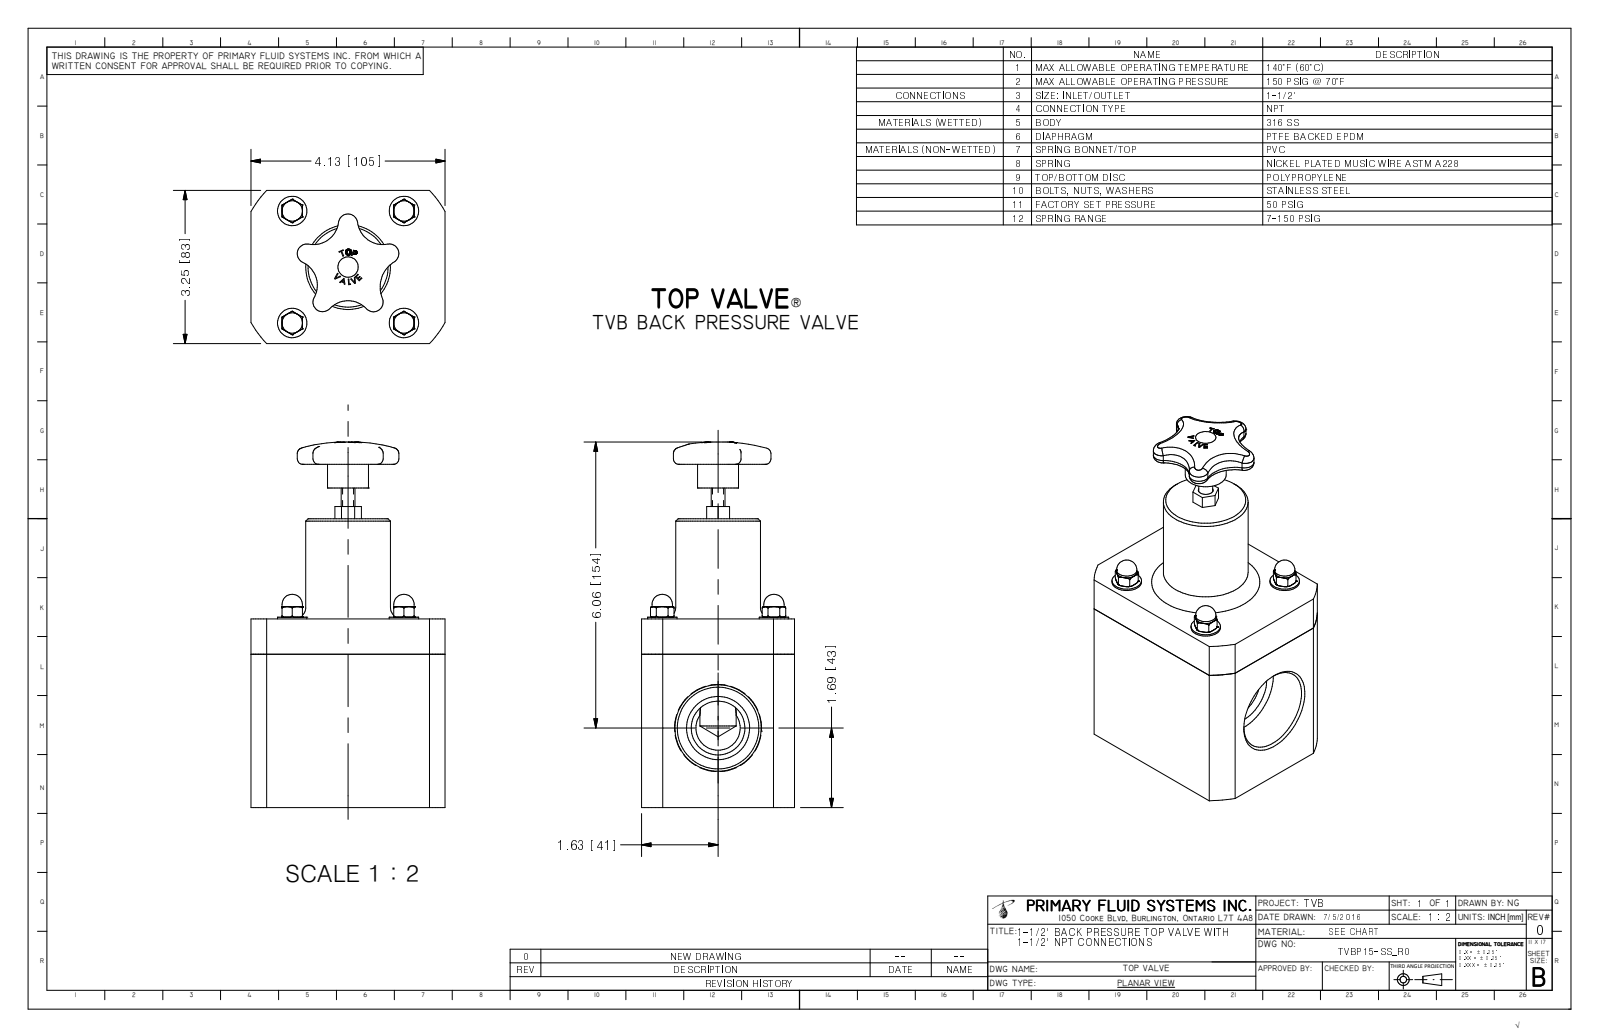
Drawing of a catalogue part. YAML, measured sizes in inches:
part_name: "TVBP15-SS-R0"
step_written_by: "Autodesk Inventor 2009 (AUTOMOTIVE_DESIGN)"
units: inches
bodies: {solids: 1, faces: 337, planar: 144, cylindrical: 45, other: 148}
overall_size: [7.752, 4.125, 3.25]
volume: 55.21
surface_area: 118.7
round_holes:
  - {diameter: 0.175, count: 4}
  - {diameter: 1.734, count: 1}
round_bosses_or_shafts:
  - {diameter: 0.625, count: 4}
  - {diameter: 0.433, count: 4}
  - {diameter: 0.375, count: 4}
  - {diameter: 1.8, count: 1}
  - {diameter: 0.87, count: 1}
  - {diameter: 0.293, count: 1}
partial_cylinders:
  - {radius: 0.085, count: 5}
  - {radius: 0.205, count: 5}
  - {radius: 0.536, count: 4}
  - {radius: 0.656, count: 4}
  - {radius: 0.625, count: 1}
  - {radius: 0.745, count: 1}
  - {radius: 2.375, count: 1}
face_to_face_distances: [3.25, 4, 4.125, 0.9, 3.225, 2.325, 6.125, 2.125, 0.433, 4.036]
hole_center_spacings: [2.375, 2.375, 3.359]
